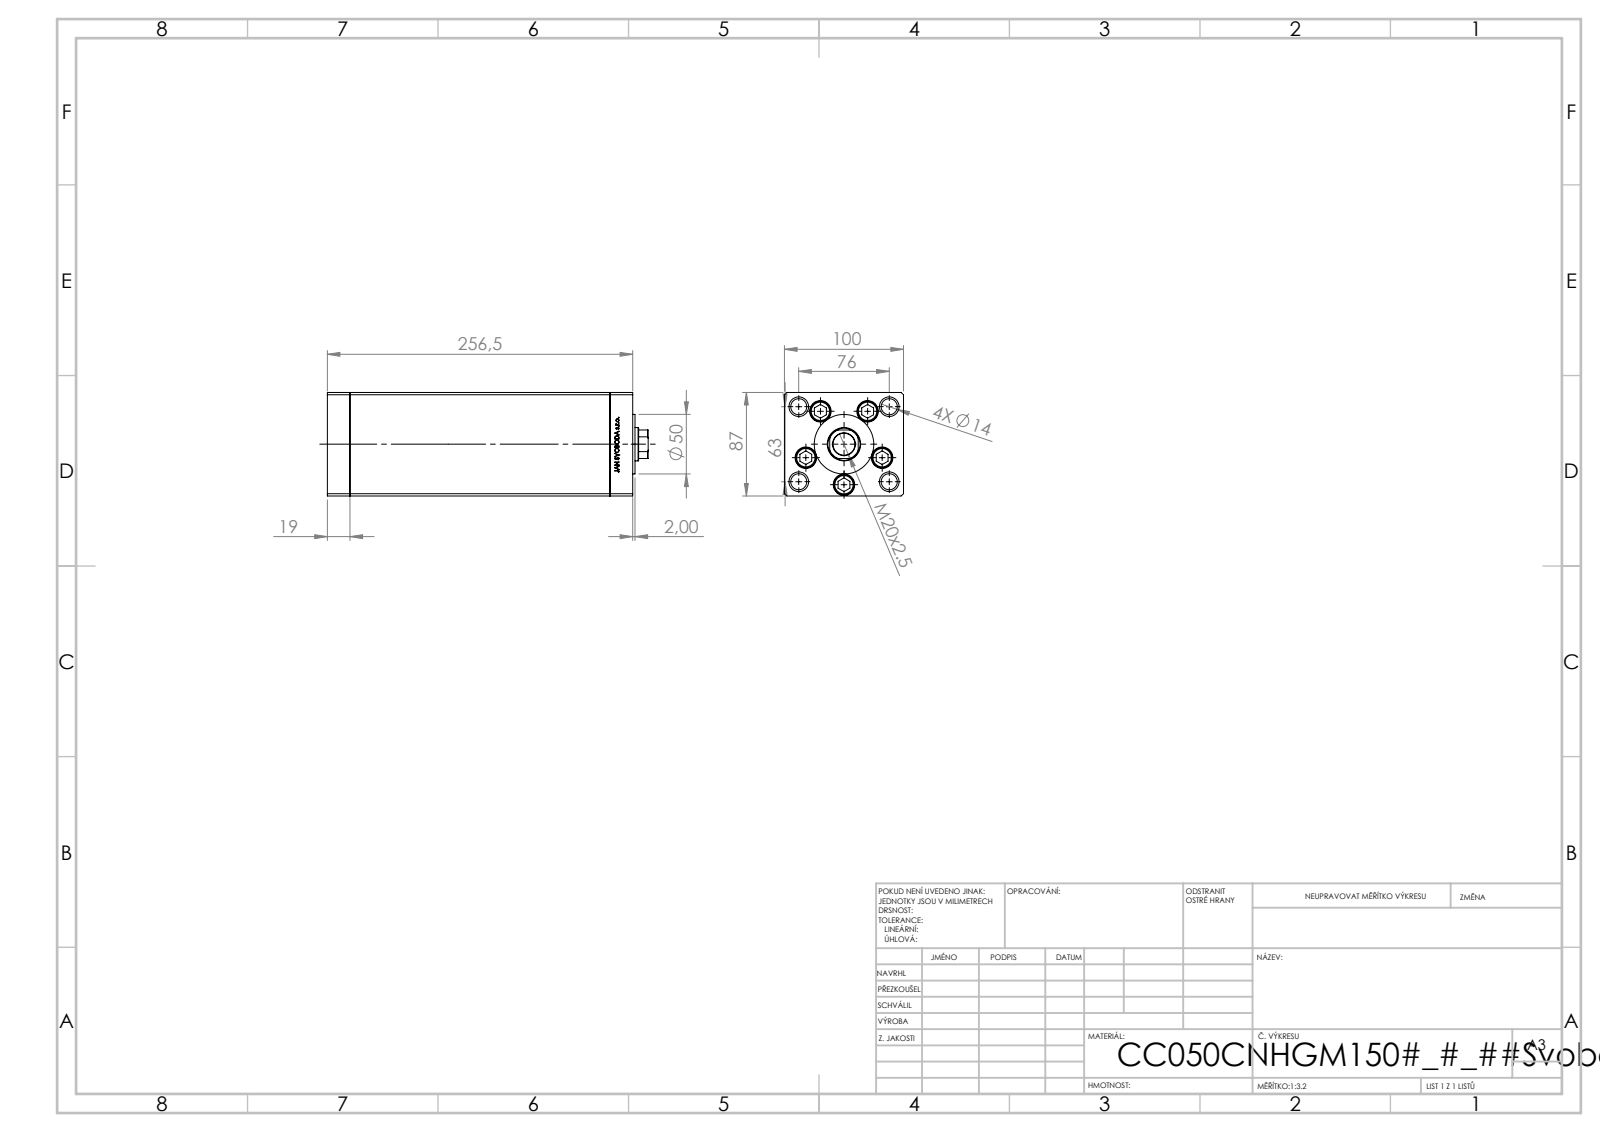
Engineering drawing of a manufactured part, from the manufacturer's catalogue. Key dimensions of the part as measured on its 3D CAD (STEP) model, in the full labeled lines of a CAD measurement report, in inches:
Part name (STEP PRODUCT): V220C_C MIDDLE; V220C FRONT; V220C_VC_C; ALLEN BOLT (+1 more)
STEP written by: SolidWorks 2019 (CONFIG_CONTROL_DESIGN)
Units: inches
Bodies: 13 solids, 1186 faces (548 planar, 176 cylindrical, 462 other)
Overall size (bounding box): 10.61 × 3.937 × 3.425
Volume: 111.1 in³ · Surface area: 433.2 in²
Round holes (diameter × count): ⌀0.531 ×9, ⌀0.709 ×5, ⌀0.079 ×4, ⌀0.472 ×4, ⌀0.518 ×4, ⌀0.65 ×4, ⌀0.669 ×1, ⌀0.728 ×1, ⌀1.102 ×1
Round bosses / shafts (diameter × count): ⌀0.315 ×5, ⌀0.669 ×4, ⌀1.969 ×1
Partial cylindrical surfaces — rounded edges, fillets, slot ends (radius × count): R0.037 ×2, R0.531 ×1
Main face-to-face distances: 3.937, 3.425, 0.748, 8.602, 9.35, 1.348, 10.098, 8.75, 8.002, 0.6
Hole centre spacings: 1.339, 1.943, 0.732, 0.828, 1.499, 1.546, 1.607, 1.702
